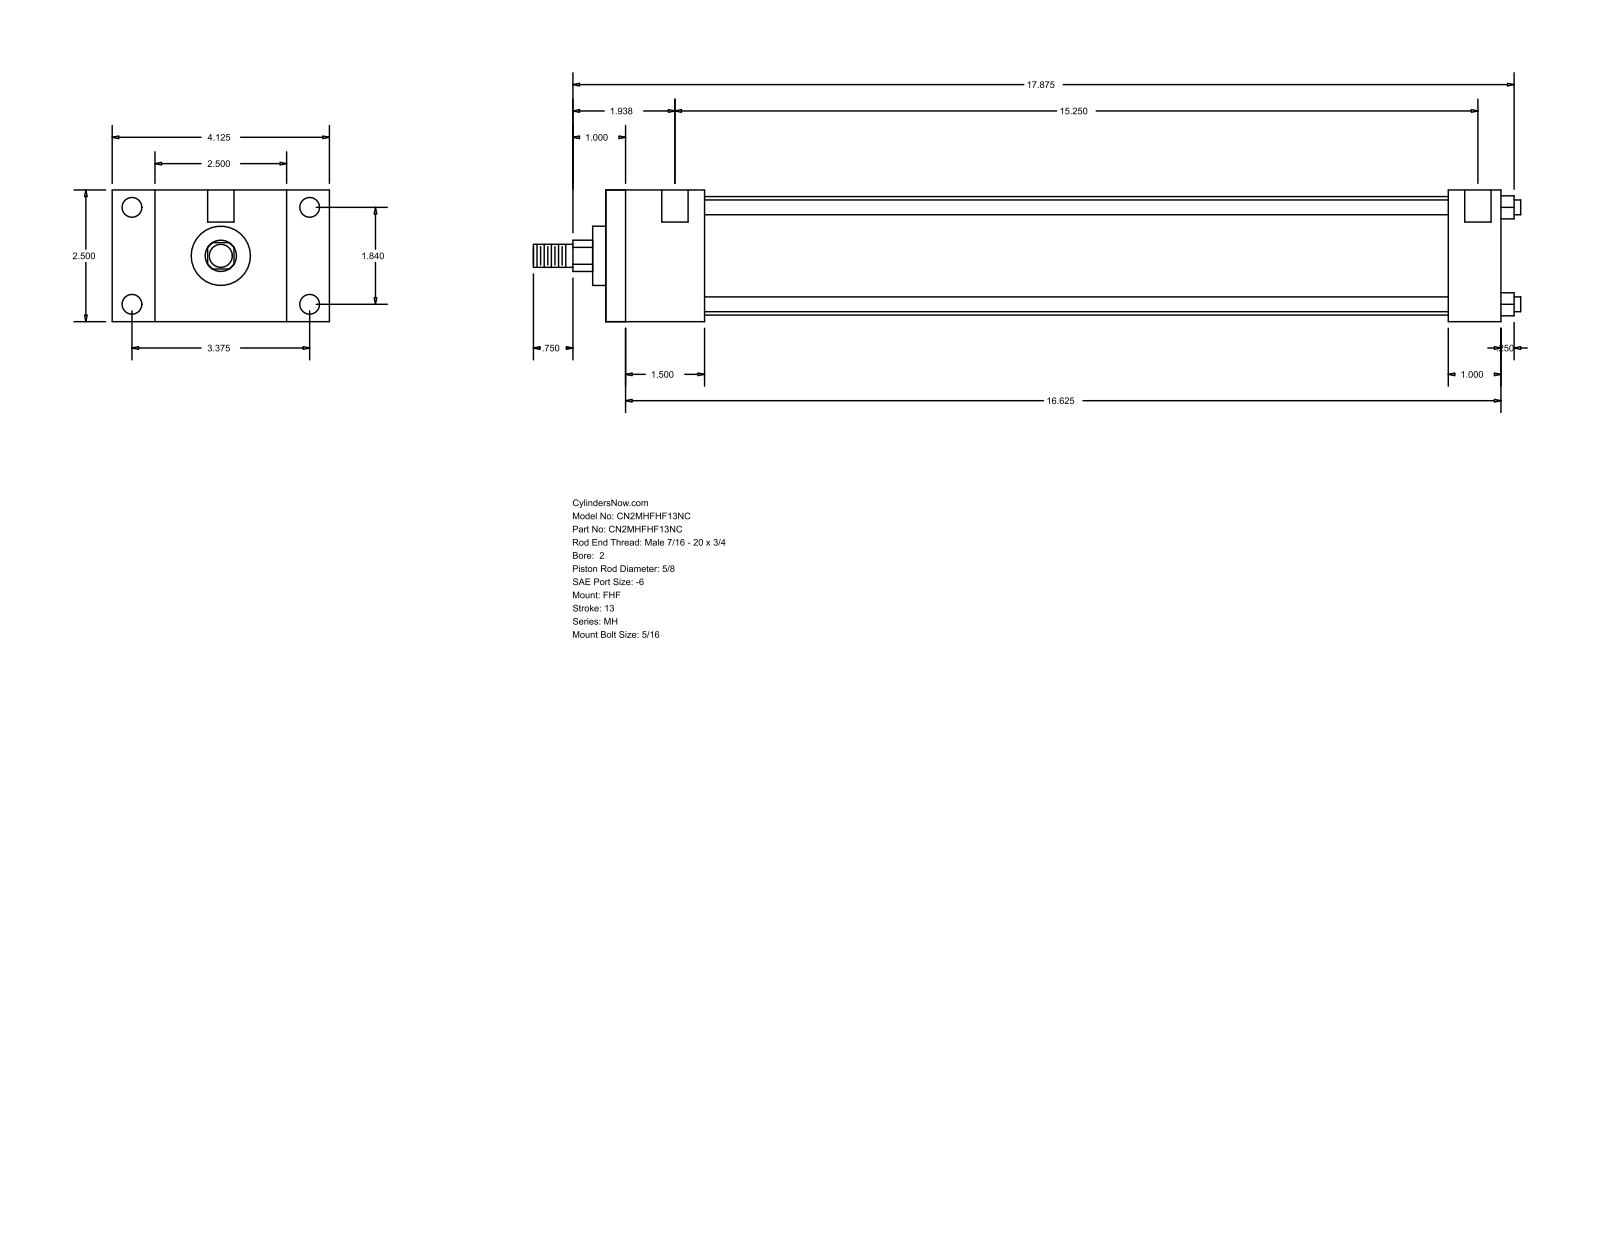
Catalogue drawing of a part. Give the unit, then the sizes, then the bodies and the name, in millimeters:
Units: millimetres
Overall size (bounding box): 476.25 × 104.78 × 63.5
Round holes (diameter × count): ⌀5.56 ×4, ⌀9.53 ×4, ⌀12.7 ×2
Round bosses / shafts (diameter × count): ⌀7.14 ×4, ⌀57.15 ×1, ⌀28.57 ×1, ⌀15.88 ×1, ⌀11.11 ×1
Partial cylindrical surfaces — rounded edges, fillets, slot ends (radius × count): R7.54 ×1
Main face-to-face distances: 63.5, 47.62, 431.8, 384.18, 20.64, 84.14, 104.78, 406.39, 358.77, 25.41
Hole centre spacings: 46.74, 85.72, 97.63, 395.29, 3.18, 4.76, 387.35, 390.53
Bodies: 0 solids, 88 faces (60 planar, 28 cylindrical, 0 other)
Part name (STEP PRODUCT): MH_FHF__0200_0.625
STEP written by: GSSL Pune (CONFIG_CONTROL_DESIGN)
